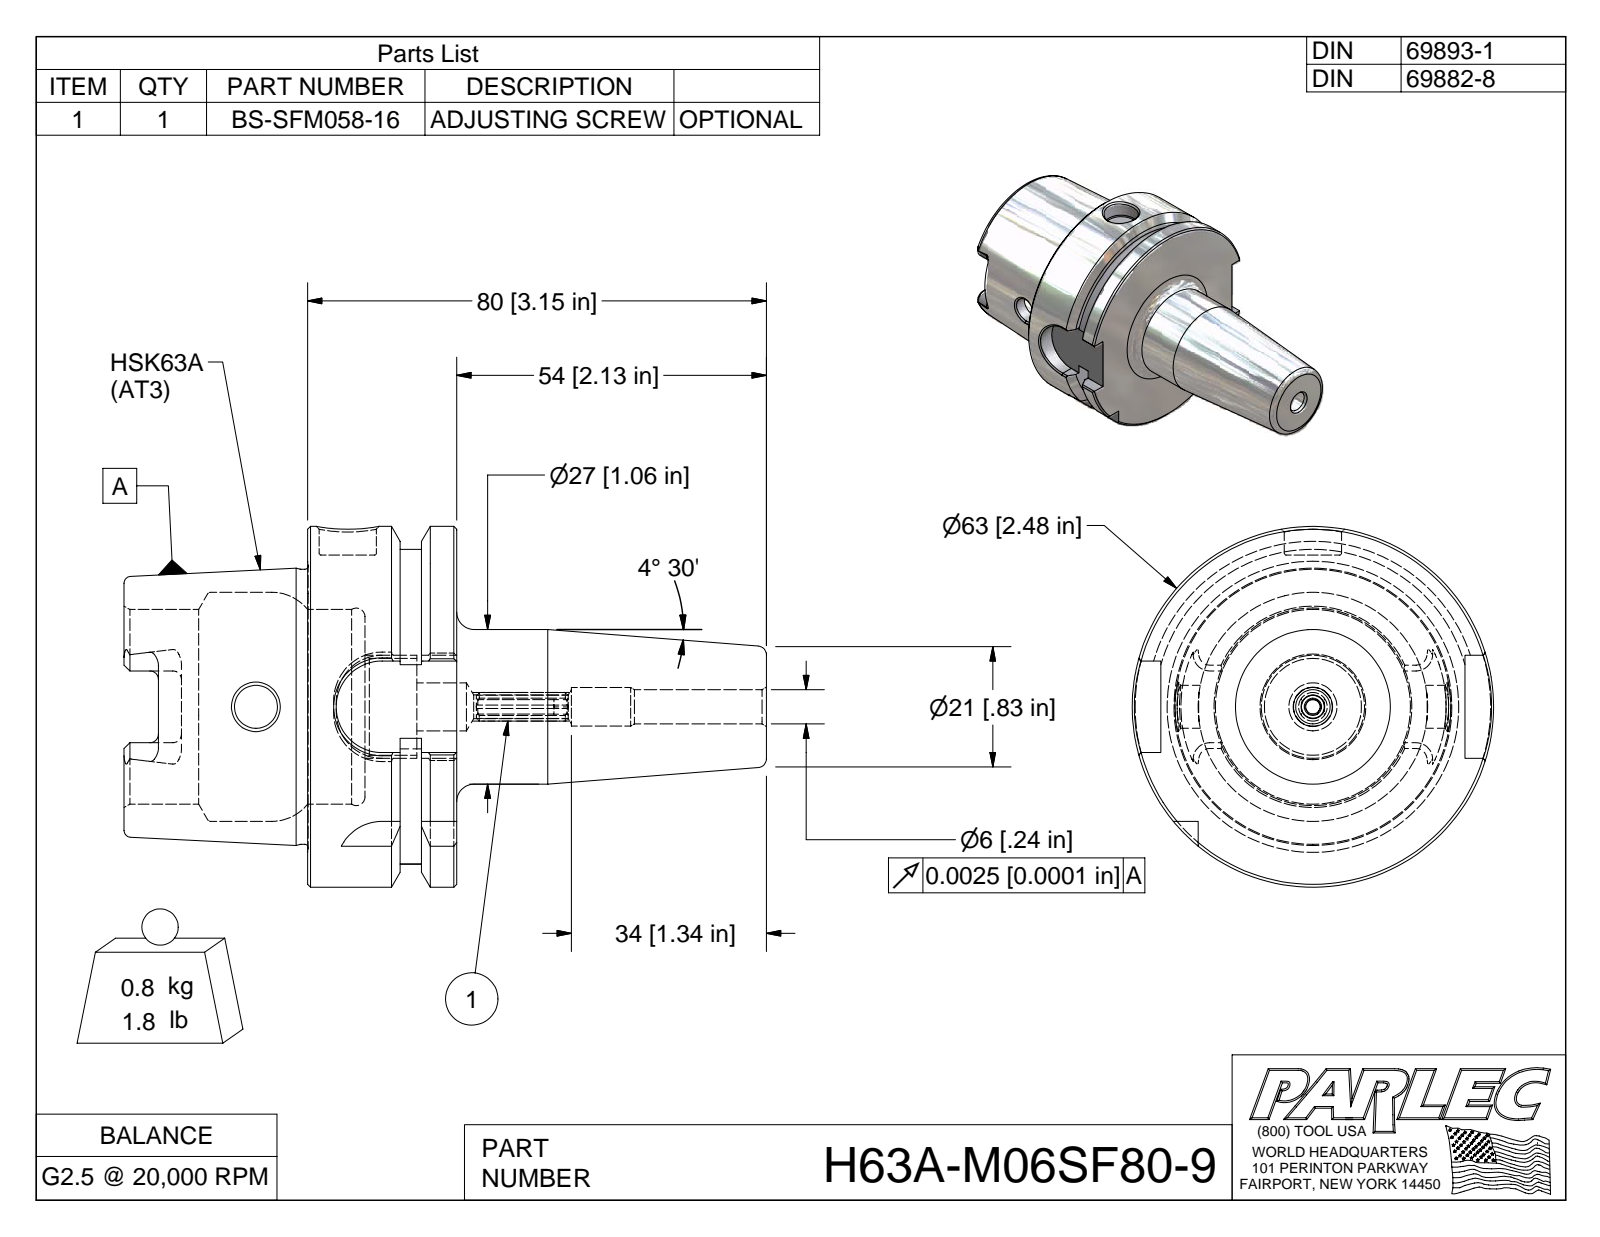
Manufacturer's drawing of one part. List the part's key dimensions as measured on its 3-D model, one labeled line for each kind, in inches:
Part name (STEP PRODUCT): H63A-M06SF80-9; H63A-M06SF80-9-1; BS-SFM058-16
STEP written by: Autodesk Inventor 2009 (AUTOMOTIVE_DESIGN)
Units: inches
Bodies: 2 solids, 157 faces (58 planar, 35 cylindrical, 64 other)
Overall size (bounding box): 4.409 × 2.48 × 2.48
Volume: 6.533 in³ · Surface area: 42.73 in²
Round holes (diameter × count): ⌀0.236 ×1, ⌀0.266 ×1, ⌀0.295 ×1, ⌀0.394 ×1, ⌀0.666 ×1, ⌀1.339 ×1, ⌀1.575 ×1
Round bosses / shafts (diameter × count): ⌀2.48 ×1, ⌀1.891 ×1, ⌀1.063 ×1
Partial cylindrical surfaces — rounded edges, fillets, slot ends (radius × count): R0.059 ×6, R0.113 ×4, R0.315 ×4, R0.098 ×1, R1.083 ×1
Main face-to-face distances: 1.024, 0.241, 0.389, 0.394, 0.63, 1.26, 1.654, 2.283, 1.894, 0.635
